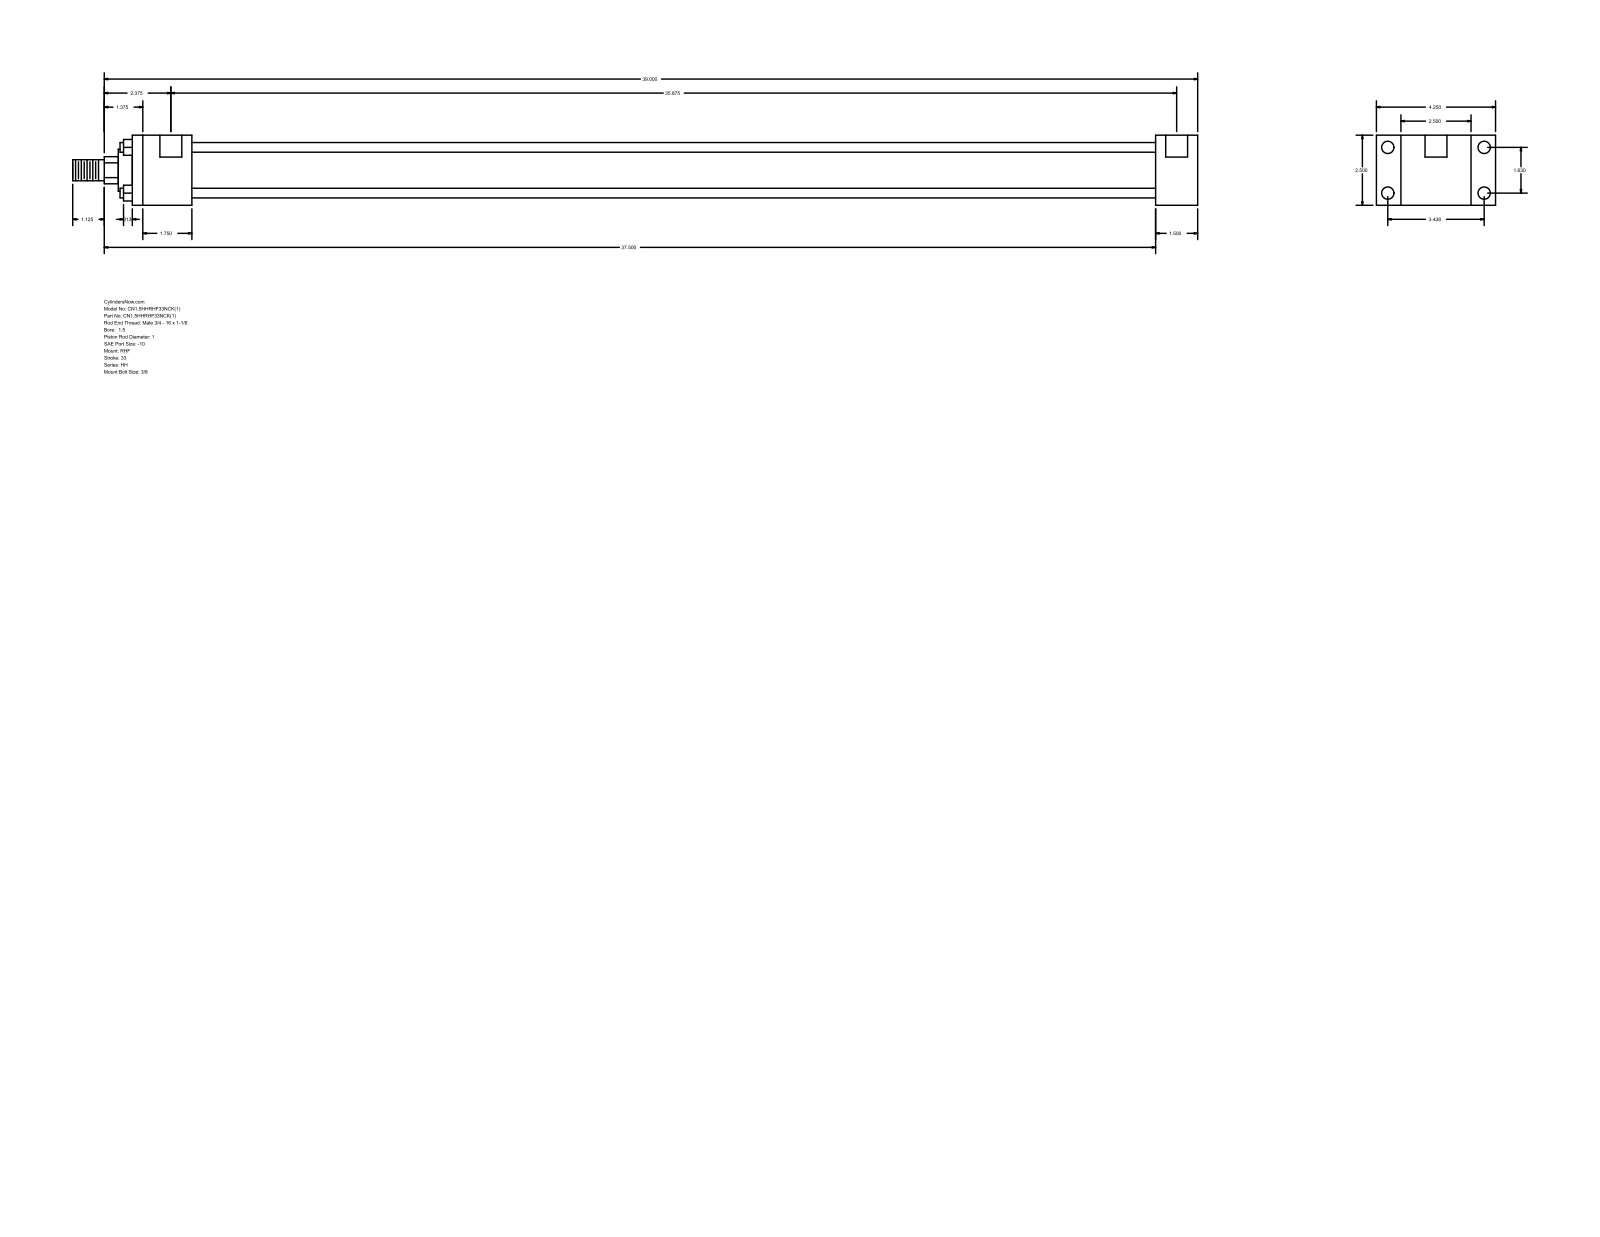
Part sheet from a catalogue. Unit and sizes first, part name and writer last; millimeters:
Units: millimetres
Overall size (bounding box): 1019.17 × 107.95 × 63.5
Round holes (diameter × count): ⌀5.56 ×4, ⌀11.13 ×4, ⌀19.84 ×2
Round bosses / shafts (diameter × count): ⌀8.76 ×4, ⌀44.45 ×1, ⌀38.1 ×1, ⌀25.4 ×1, ⌀19.05 ×1
Partial cylindrical surfaces — rounded edges, fillets, slot ends (radius × count): R12.29 ×1
Main face-to-face distances: 63.5, 22.23, 85.73, 38.1, 107.96, 873.12, 911.22, 53.98, 927.1, 965.2
Hole centre spacings: 1.59, 41.4, 87.32, 96.64, 912.81, 914.4, 911.22
Bodies: 0 solids, 88 faces (60 planar, 28 cylindrical, 0 other)
Part name (STEP PRODUCT): HH_RHF__0150_1
STEP written by: GSSL Pune (CONFIG_CONTROL_DESIGN)
